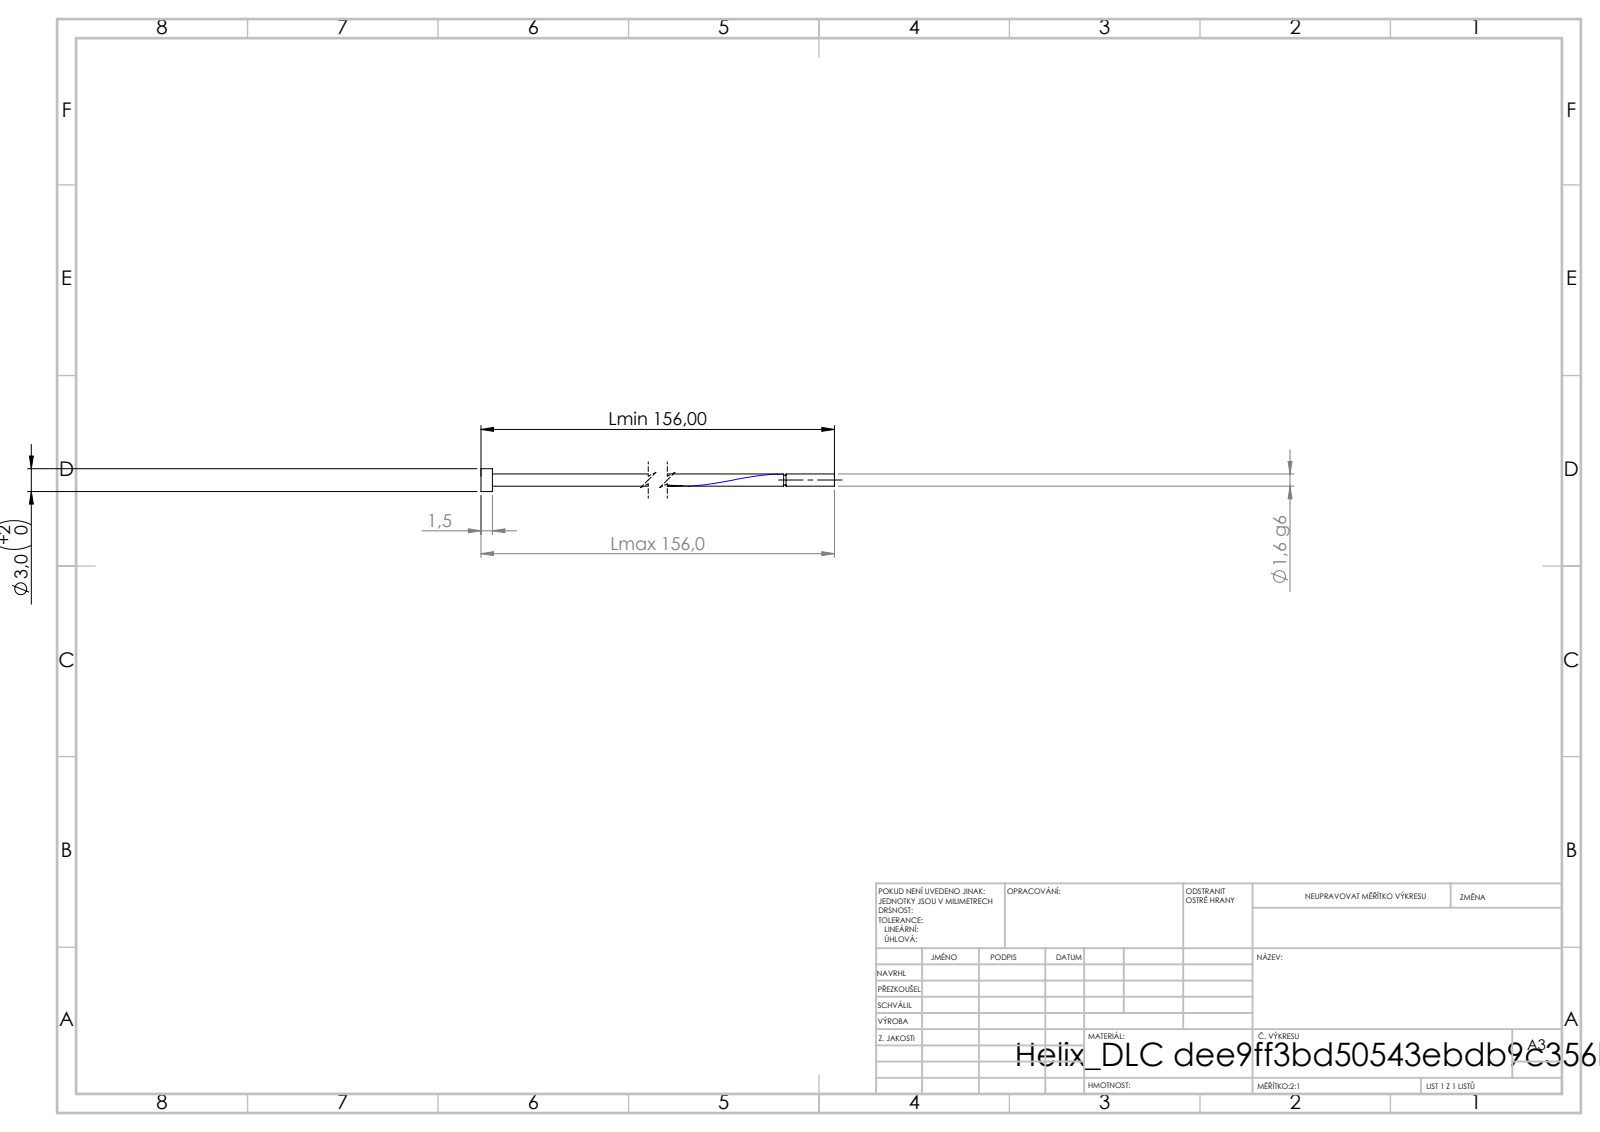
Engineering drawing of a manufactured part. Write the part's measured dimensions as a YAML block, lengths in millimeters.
step_written_by: "SolidWorks 2019 (CONFIG_CONTROL_DESIGN)"
units: millimeters
bodies: {solids: 1, faces: 16, planar: 6, cylindrical: 9, other: 1}
overall_size: [156, 3, 3]
volume: 389
surface_area: 1086
round_bosses_or_shafts:
  - {diameter: 3, count: 1}
  - {diameter: 1.6, count: 1}
  - {diameter: 1.28, count: 1}
face_to_face_distances: [1.5, 156, 154.5, 149.65, 148.15, 6.35, 149.33, 147.83, 0.32, 6.67]
